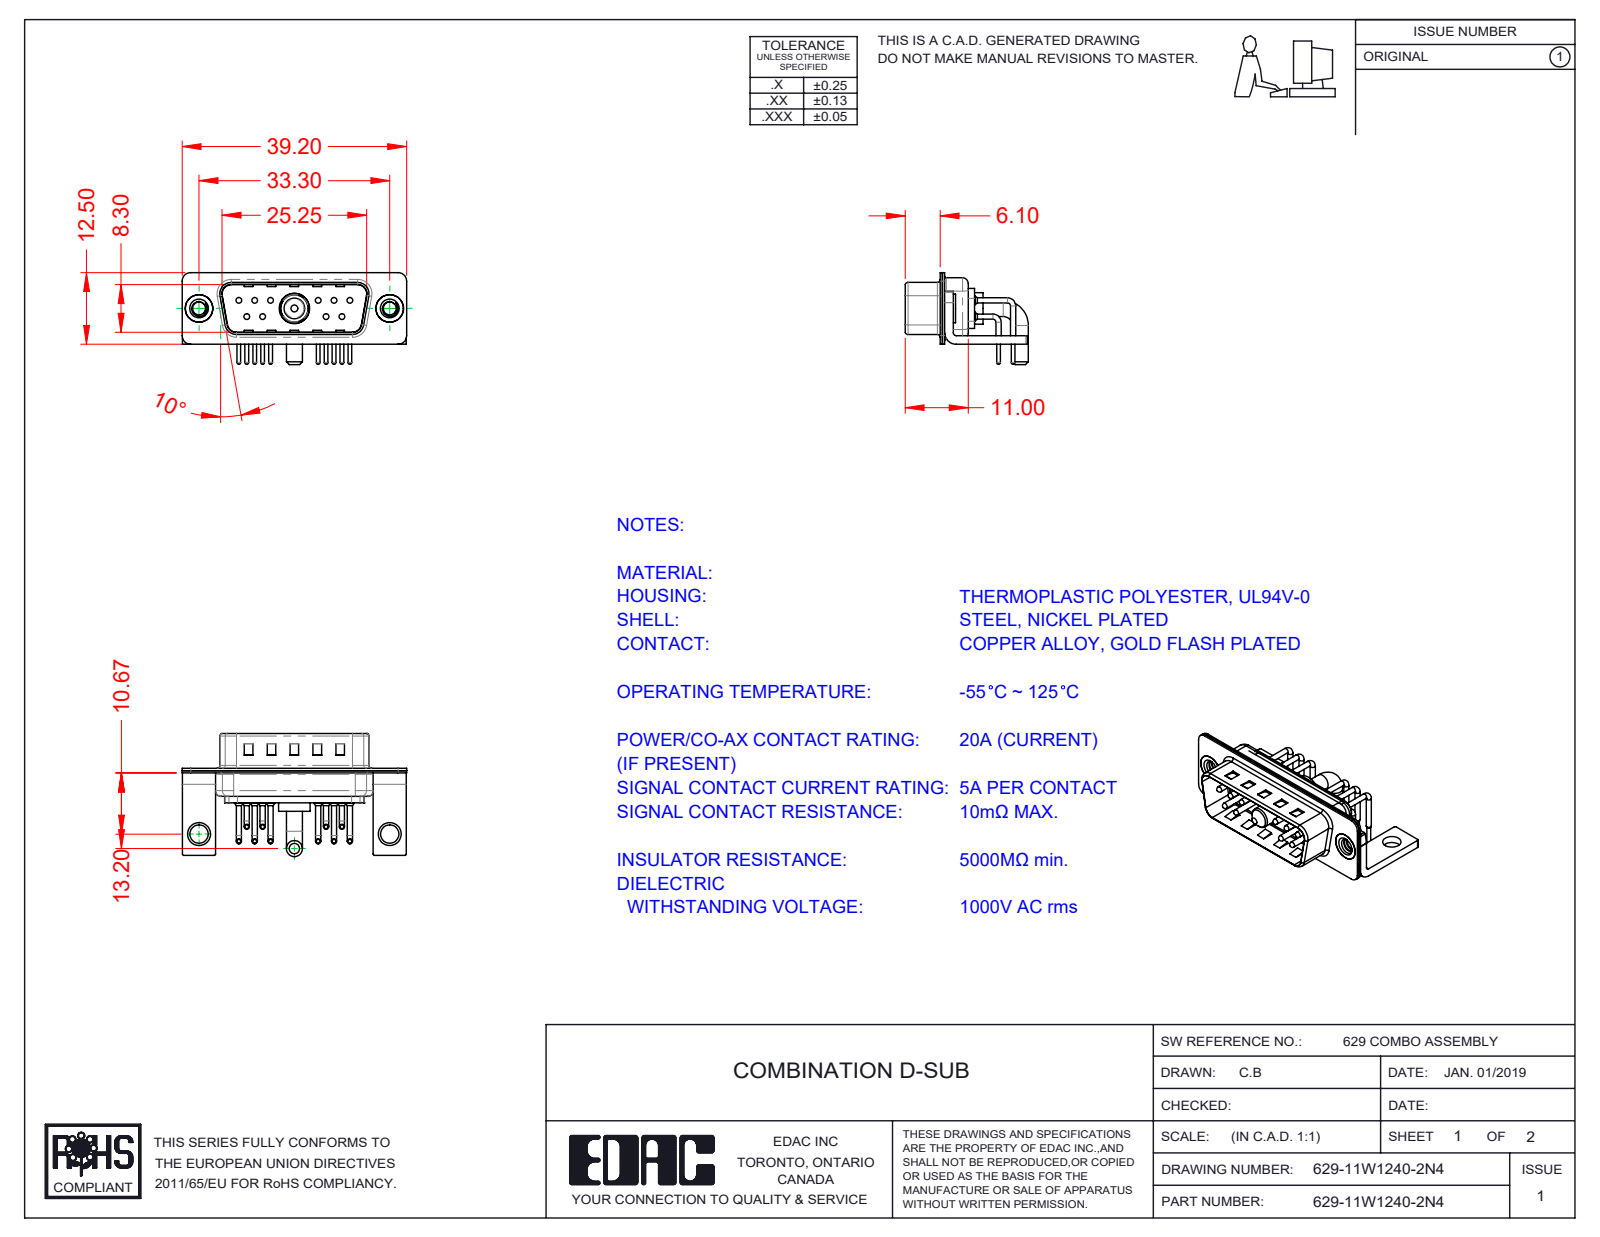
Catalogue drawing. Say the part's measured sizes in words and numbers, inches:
The part is named "629Combo Contact Row 2; 629Combo Housing_11W1; 629Combo Contact Row 1; 629Combo Shell Rear_15 Contacts (+5 more)". Its 3-D file was written by "SolidWorks 2020 (CONFIG_CONTROL_DESIGN)". It is 19 solids with 1536 faces: 818 planar, 536 cylindrical and 182 other. Overall it measures 1.543 by 0.846 by 0.632 inches. Its volume is 0.142 cubic inches and its surface area 9.021 square inches. Round holes: 10 of diameter 0.03, 10 of diameter 0.063, 10 of diameter 0.079, 2 of diameter 0.089, 2 of diameter 0.126, 2 of diameter 0.157, 2 of diameter 0.189, 1 of diameter 0.191, 1 of diameter 0.209. Round bosses or shafts: 20 of diameter 0.035, 10 of diameter 0.059, 10 of diameter 0.039, 10 of diameter 0.026, 2 of diameter 0.197, 2 of diameter 0.193, 2 of diameter 0.11, 1 of diameter 0.217. Partial cylindrical surfaces (rounded edges, fillets, slot ends): 16 of radius 0.01, 16 of radius 0.059, 13 of radius 0.079, 10 of radius 0.04, 9 of radius 0.02, 8 of radius 0.063, 7 of radius 0.039, 4 of radius 0.024. The main face-to-face distances are 0.016, 0.031, 0.059, 0.374, 0.358, 0.343, 0.39, 0.024, 0.075, 0.205. The hole center spacings are 0.124, 0.109, 0.545, 0.436, 0.654, 0.198, 0.198, 0.218.
